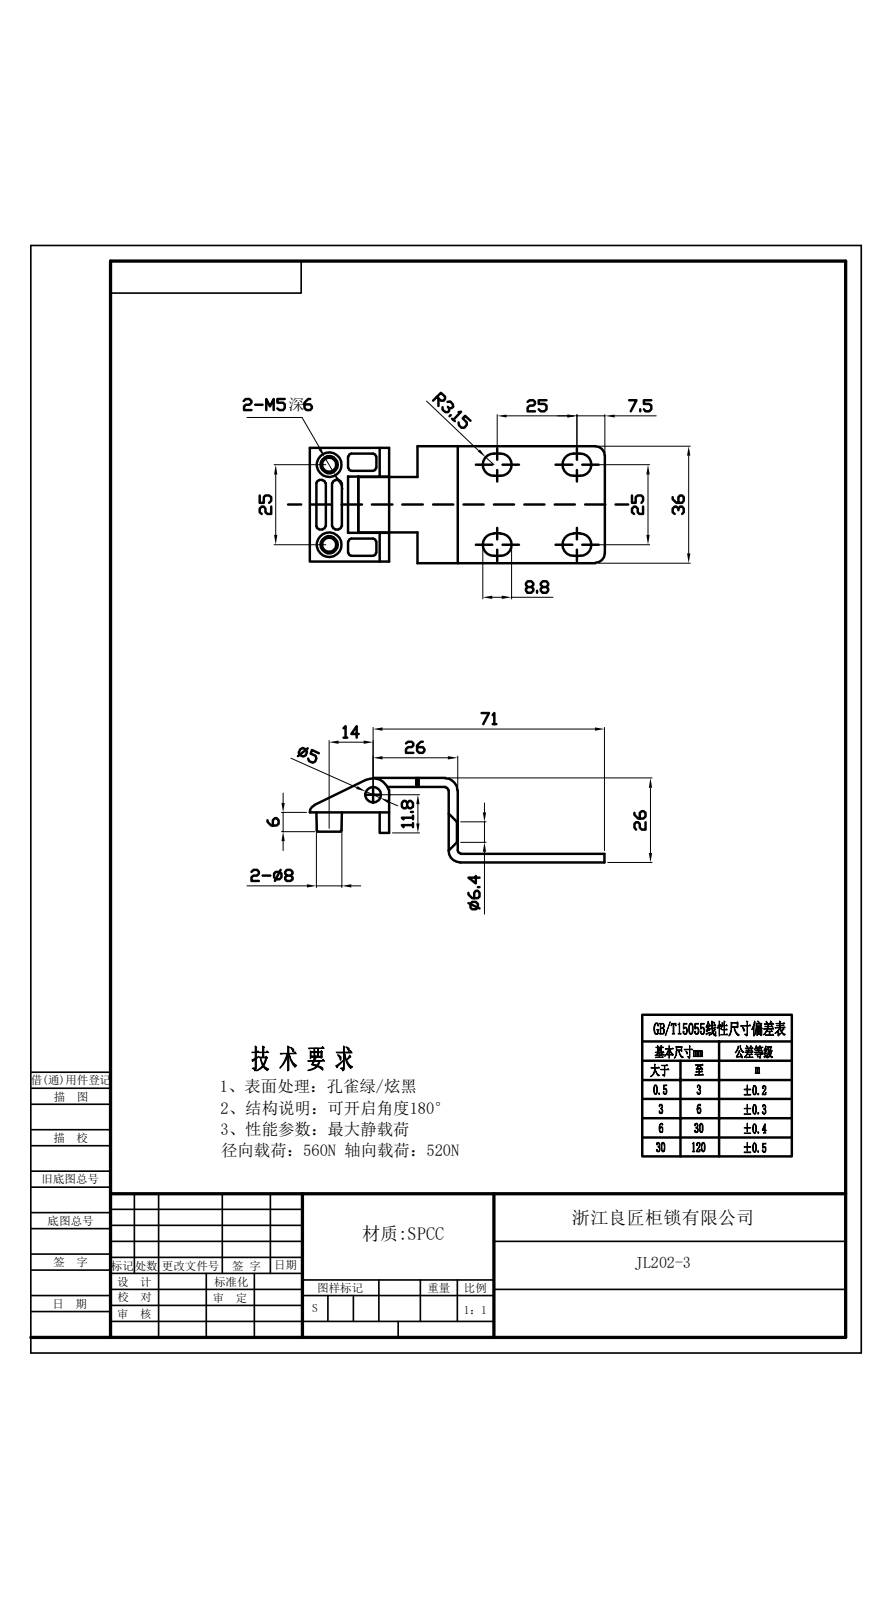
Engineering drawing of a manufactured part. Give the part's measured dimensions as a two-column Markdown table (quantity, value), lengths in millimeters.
| quantity | value |
| --- | --- |
| STEP written by | Rhino 8.5 (CONFIG_CONTROL_DESIGN) |
| units | millimeters |
| bodies | 3 solids, 104 faces (52 planar, 51 cylindrical, 1 other) |
| overall size | 92.25 × 36.73 × 26.5 |
| volume | 13 637 mm³ |
| surface area | 11 230 mm² |
| round holes (diameter × count) | 5.5 × 2, 5 × 1 |
| round bosses / shafts (diameter × count) | 7.9 × 2, 4.5 × 2, 10.5 × 1 |
| partial cylindrical surfaces (radius × count) | 1 × 18, 3.5 × 8, 3 × 2, 3.8 × 2, 2.5 × 1 |
| main face-to-face distances | 2.8, 26.5, 23.7, 15.75, 12.95, 10.75, 8.9, 26.37, 26.6, 18.65 |
| hole center spacings | 25.36 |
